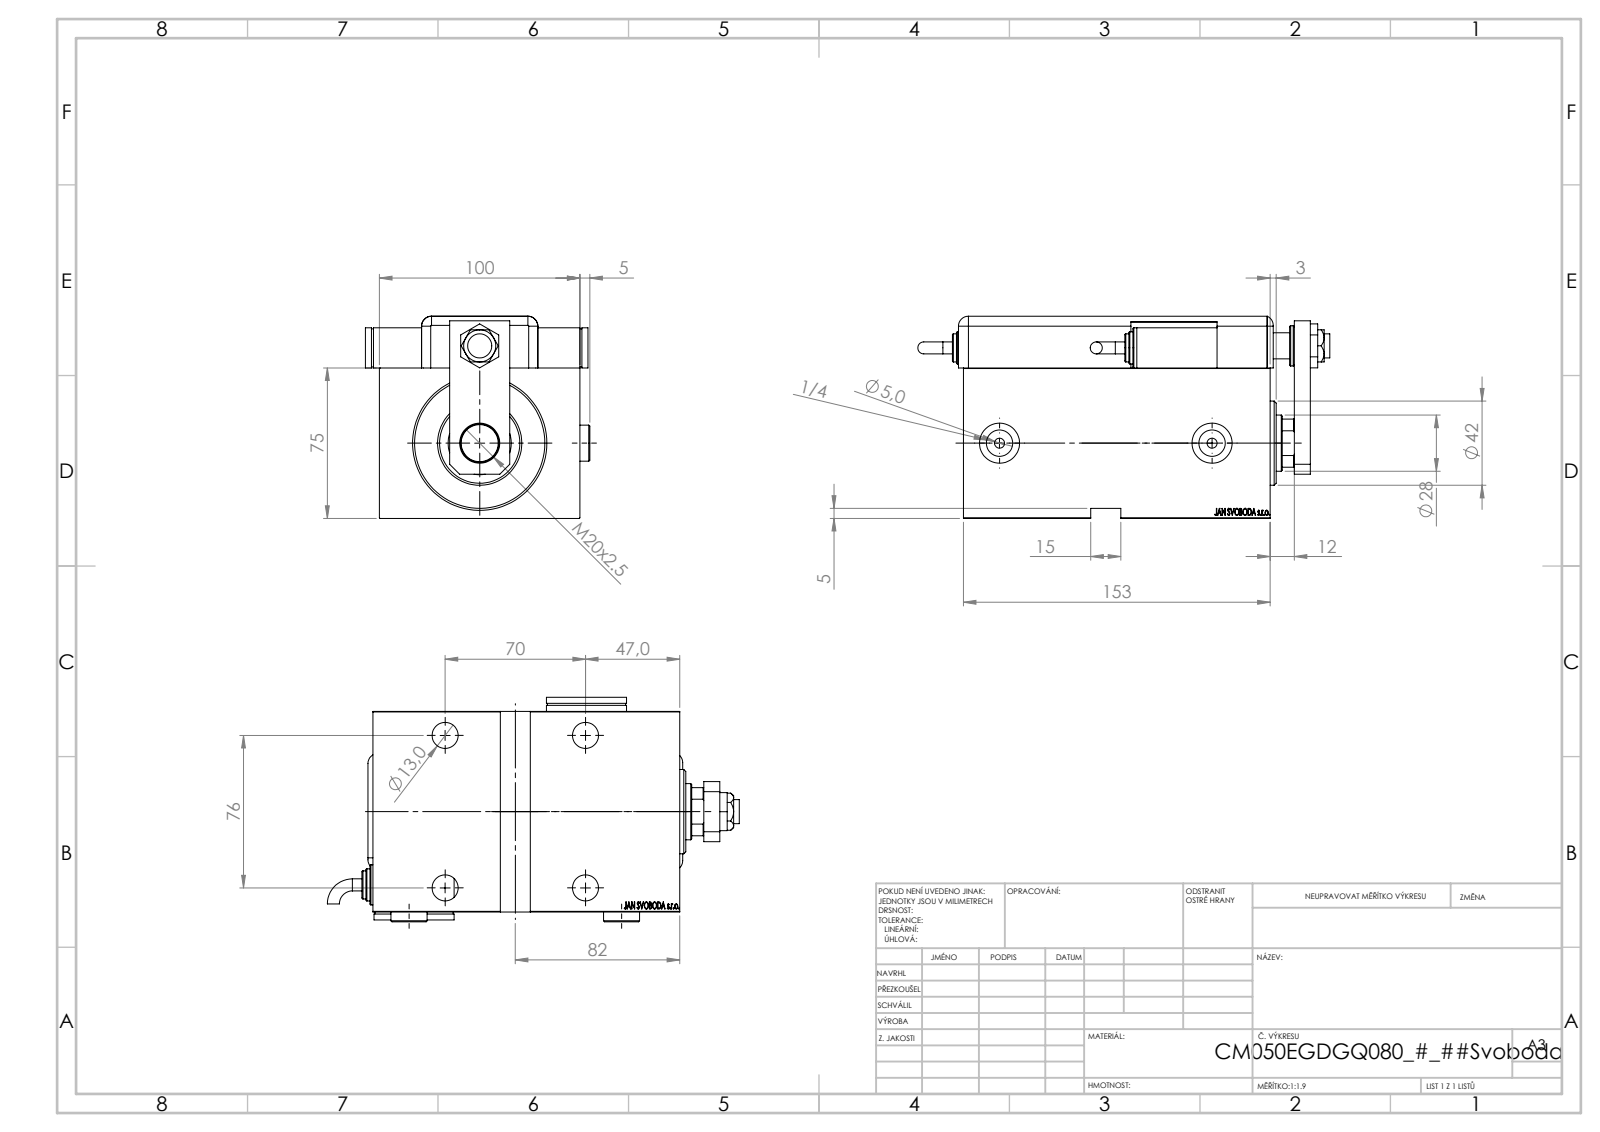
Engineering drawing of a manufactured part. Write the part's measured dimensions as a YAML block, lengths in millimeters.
part_name: "Zatka_OIL_PORT; V450CM_VC_B; KRYT; TYC (+8 more)"
step_written_by: "SolidWorks 2019 (CONFIG_CONTROL_DESIGN)"
units: millimeters
bodies: {solids: 15, faces: 1296, planar: 652, cylindrical: 123, other: 521}
overall_size: [205.46, 111.9, 100.8]
volume: 1150000
surface_area: 208806
round_holes:
  - {diameter: 13, count: 5}
  - {diameter: 19, count: 4}
  - {diameter: 20, count: 3}
  - {diameter: 4, count: 2}
  - {diameter: 5, count: 2}
  - {diameter: 8, count: 2}
  - {diameter: 13.16, count: 2}
  - {diameter: 12, count: 1}
  - {diameter: 14, count: 1}
  - {diameter: 18.5, count: 1}
  - {diameter: 28, count: 1}
  - {diameter: 31.5, count: 1}
round_bosses_or_shafts:
  - {diameter: 20, count: 3}
  - {diameter: 18, count: 2}
  - {diameter: 16, count: 2}
  - {diameter: 14, count: 2}
  - {diameter: 6, count: 2}
  - {diameter: 52, count: 1}
  - {diameter: 42, count: 1}
partial_cylinders:
  - {radius: 5, count: 9}
  - {radius: 10, count: 1}
  - {radius: 13.5, count: 1}
face_to_face_distances: [3, 75, 100, 100.8, 25.8, 153, 22.8, 97.8, 14, 20]
hole_center_spacings: [47.2, 61.22, 70, 76, 103.32, 111.57, 118.19, 20]
